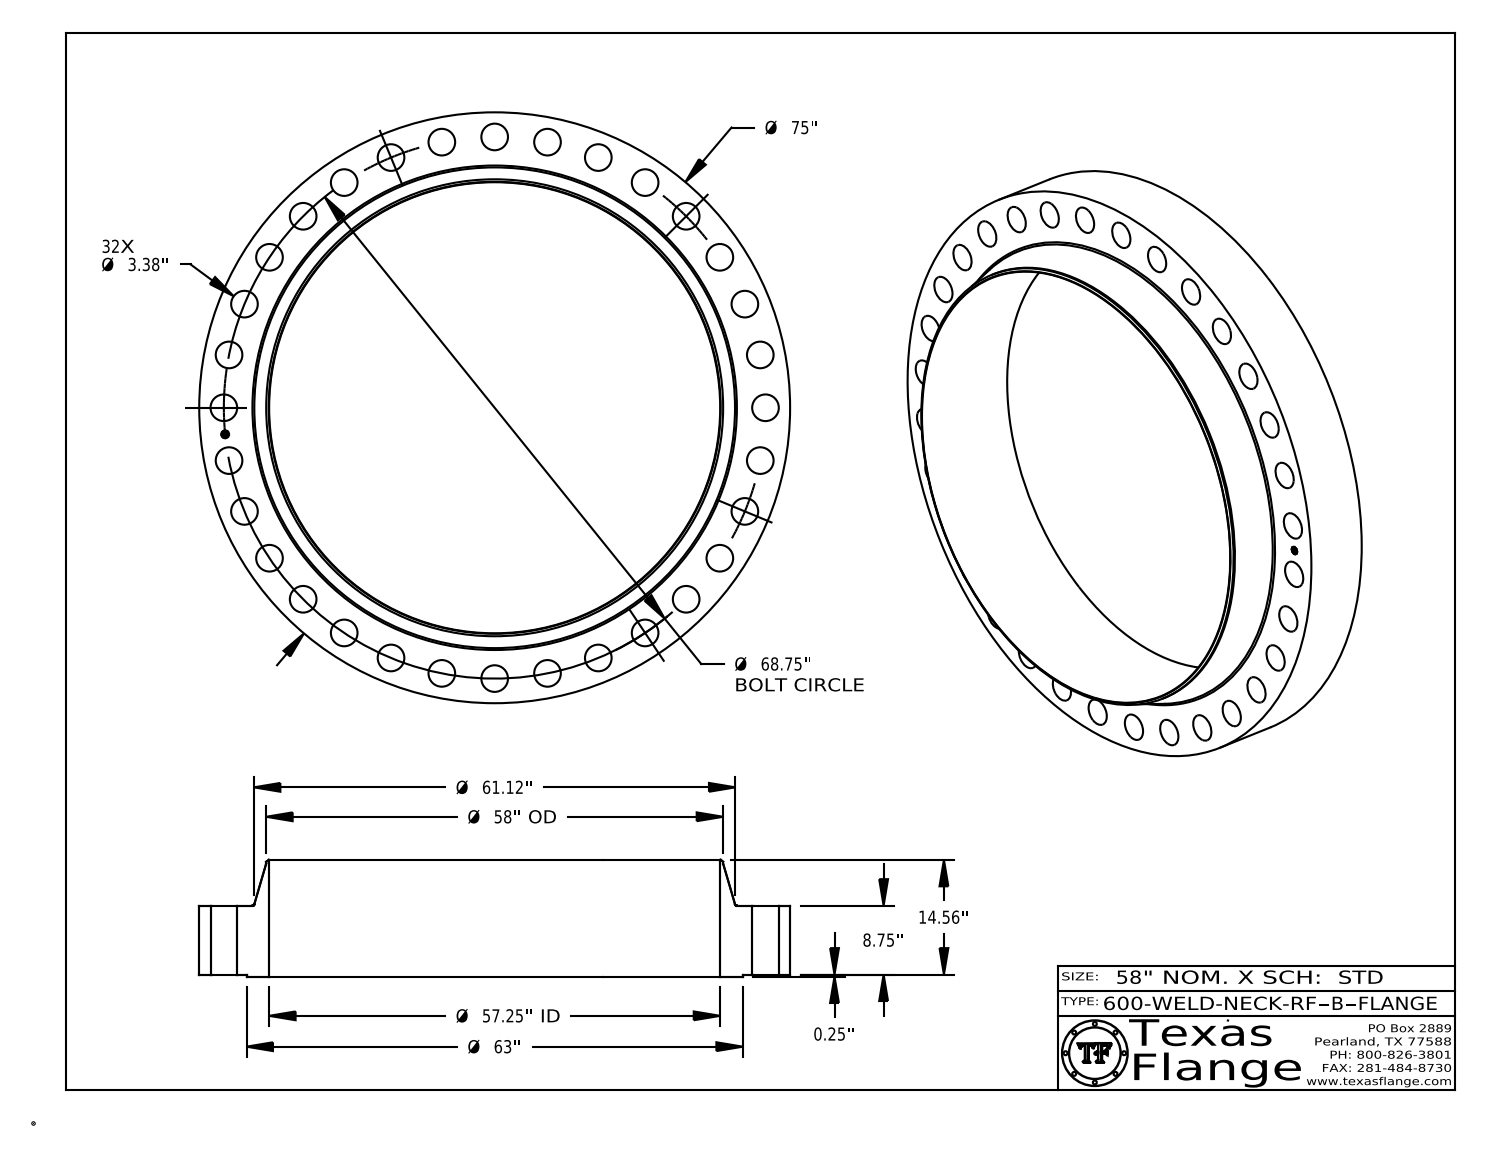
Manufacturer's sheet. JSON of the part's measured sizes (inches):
{"part_name": "600-WELD-NECK-RF, Series B", "step_written_by": "CATIA V5 STEP AP214 (AUTOMOTIVE_DESIGN)", "units": "inches", "bodies": {"solids": 1, "faces": 467, "planar": 369, "cylindrical": 92, "other": 6}, "overall_size": [75, 75, 14.81], "volume_in3": 14916, "surface_area_in2": 11657, "round_holes": [[3.38, 32], [1, 1], [57.25, 1]], "round_bosses_or_shafts": [[0.061, 8], [75, 1], [63, 1], [58, 1], [0.788, 1]], "face_to_face_distances": [8.75, 0.25, 9, 14.81, 14.56, 5.81, 0.015, 8.985, 8.735, 5.825], "hole_center_spacings": [19.957, 26.309, 65.79, 53.144, 68.419, 60.632, 6.739, 43.615]}
